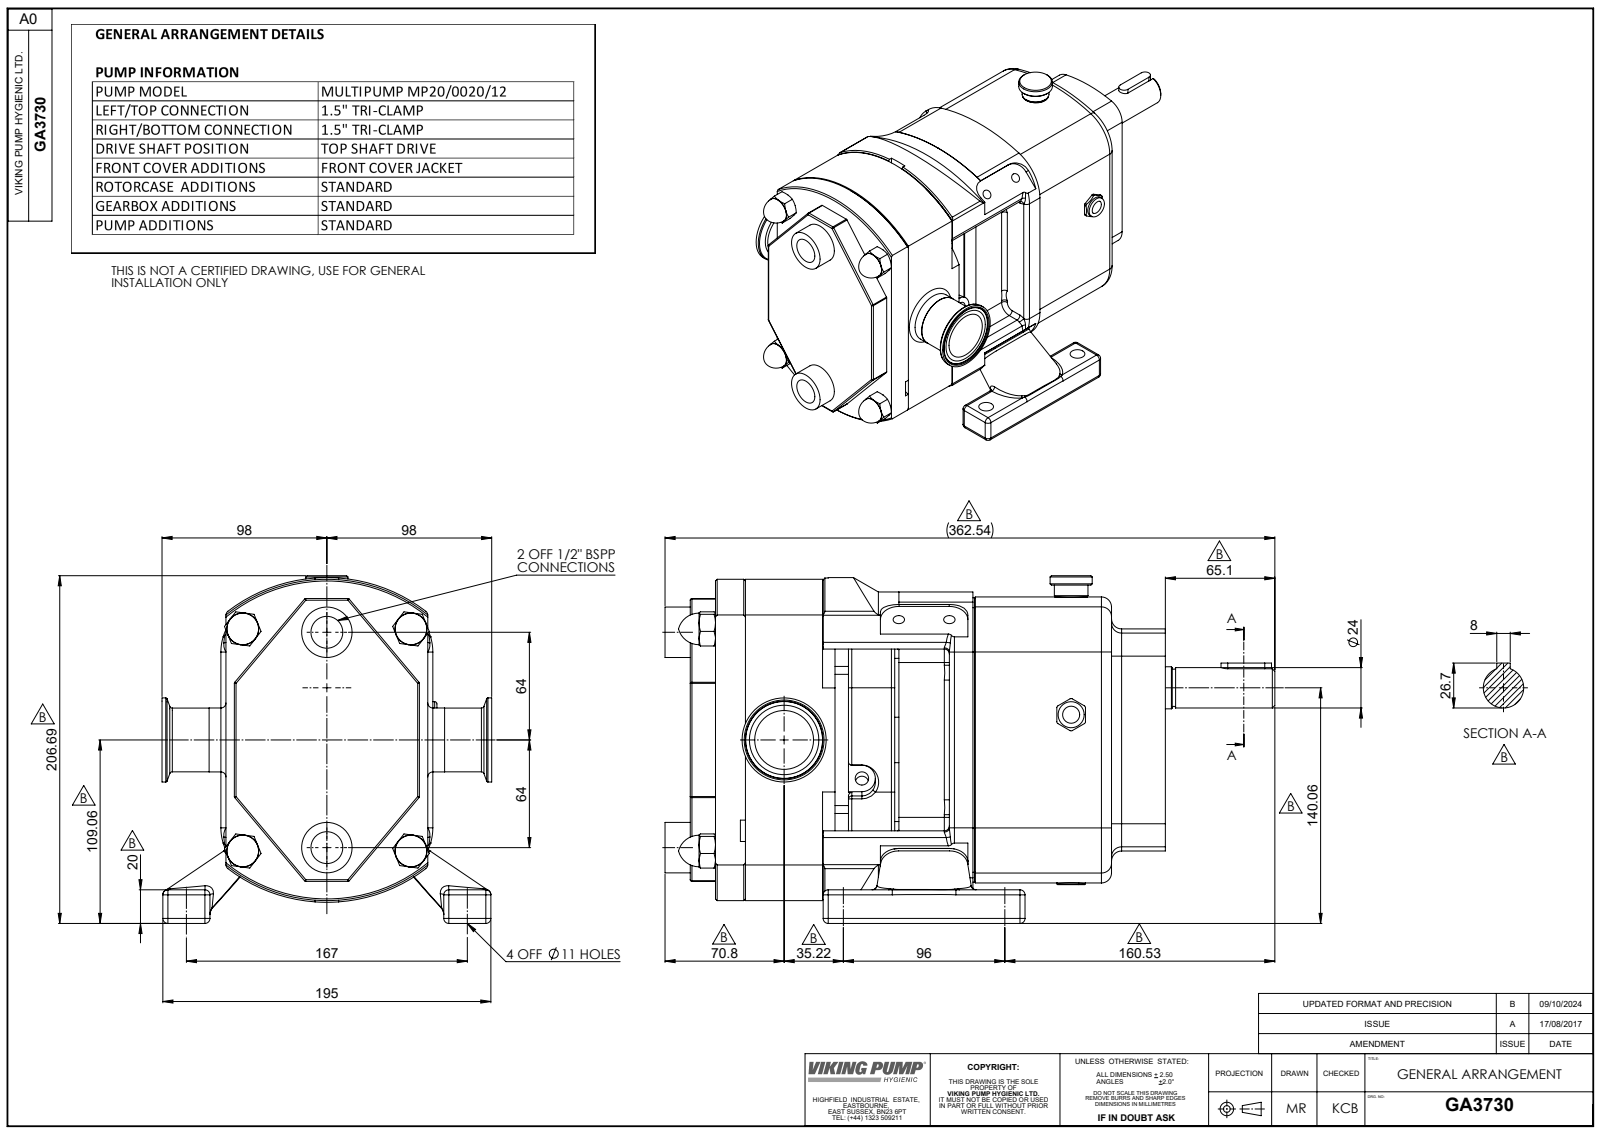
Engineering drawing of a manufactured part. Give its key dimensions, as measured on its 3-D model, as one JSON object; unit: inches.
{"part_name": "GA3730; Copy of CP-MP20 Half Inch BSP Jacket^GA3730; Copy of CP20-0020-12 H T^GA3730; Copy of Z94-5121-22 - 1.5 INCH^GA3730", "step_written_by": "SolidWorks 2023 (AUTOMOTIVE_DESIGN)", "units": "inches", "bodies": {"solids": 4, "faces": 875, "planar": 265, "cylindrical": 308, "other": 302}, "overall_size": [14.273, 8.137, 7.717], "volume_in3": 304, "surface_area_in2": 524, "round_holes": [[0.268, 4], [0.433, 4], [0.255, 3], [0.315, 2], [0.747, 2], [0.887, 1], [1.378, 1]], "round_bosses_or_shafts": [[1.378, 2], [1.181, 2], [0.669, 2], [1.969, 1], [1.496, 1], [1.492, 1], [0.985, 1], [0.984, 1]], "partial_cylinders_radius": [[0.118, 55], [0.039, 32], [0.079, 18], [0.236, 8], [0.437, 8], [0.05, 6], [0.157, 6], [0.315, 6]], "face_to_face_distances": [4.724, 0.591, 4.293, 4.883, 6.236, 10.529, 11.12, 0.984, 3.74, 0.394], "hole_center_spacings": [2.114, 1.183, 1.262, 2.52, 3.636, 3.78, 4.477, 6.576]}
